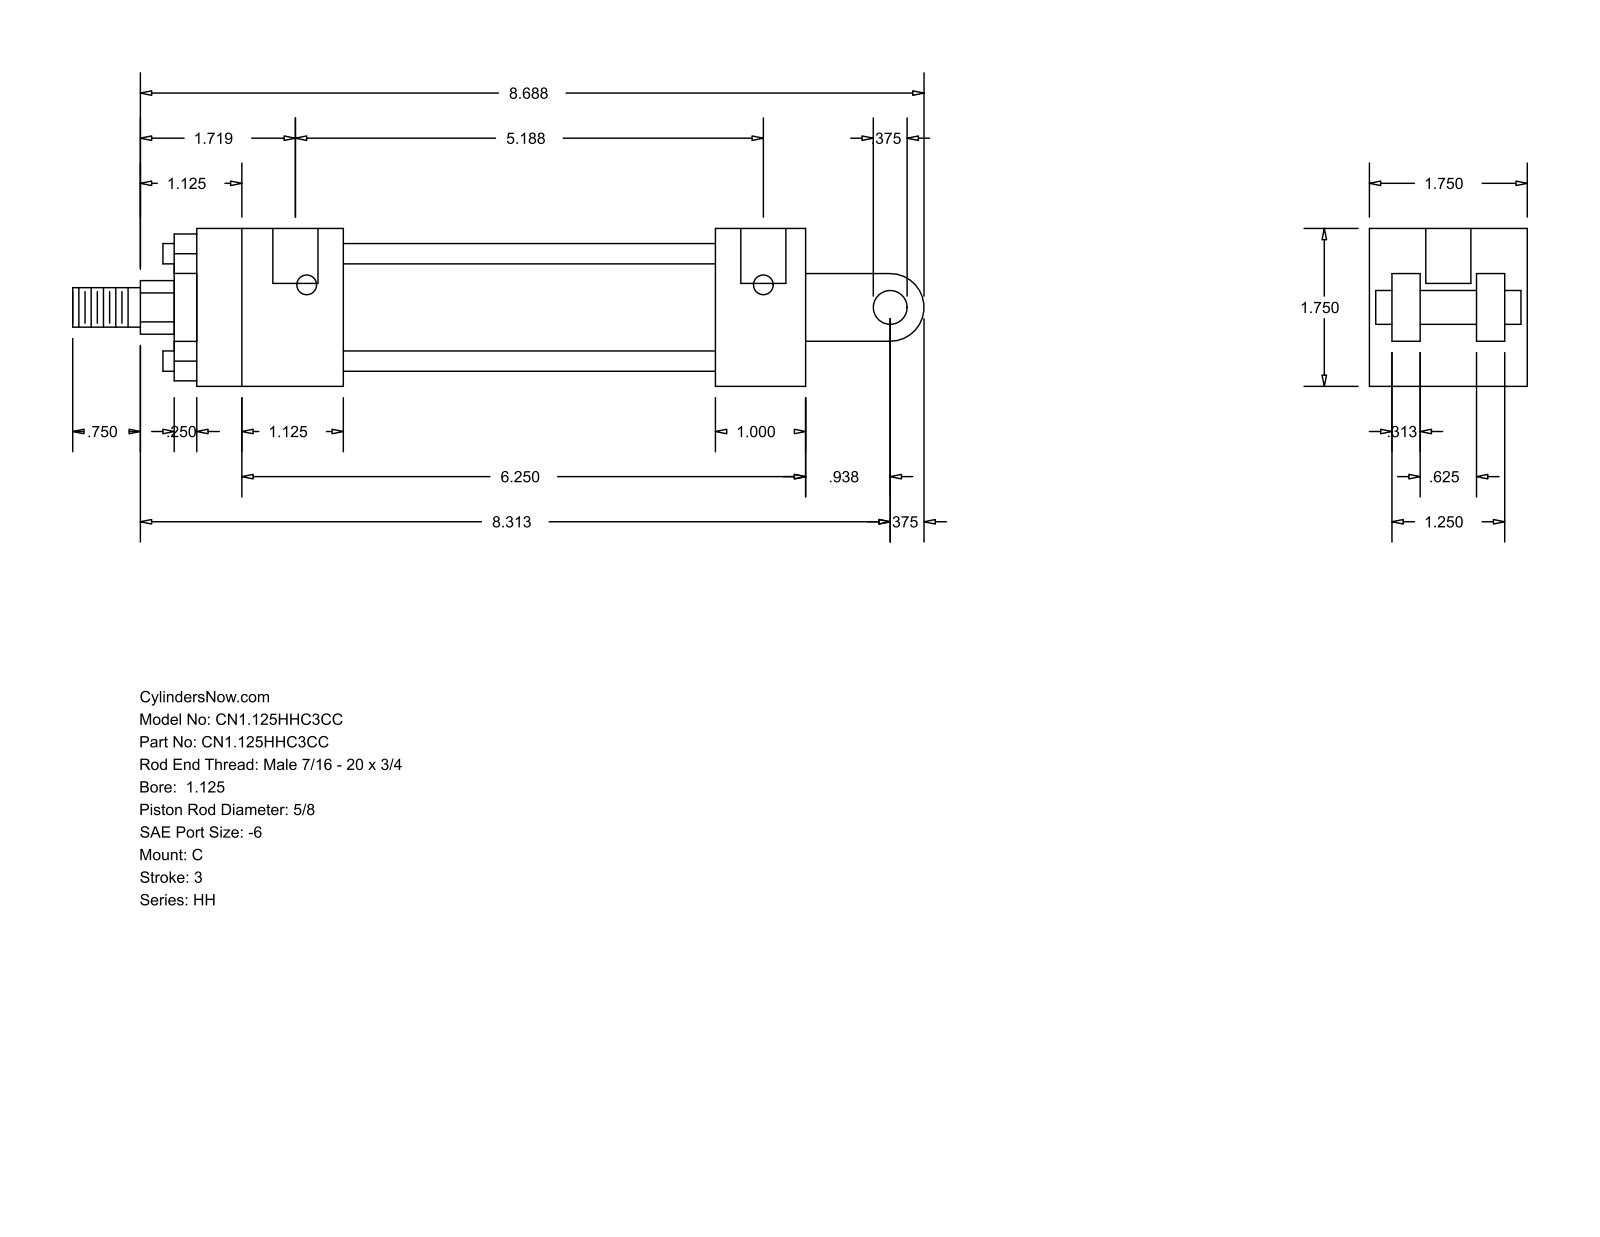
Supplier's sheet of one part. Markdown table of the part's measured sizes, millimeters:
| quantity | value |
| --- | --- |
| part name | HH_C__0112_0.625 |
| STEP written by | GSSL Pune (CONFIG_CONTROL_DESIGN) |
| units | millimeters |
| bodies | 0 solids, 99 faces (70 planar, 29 cylindrical, 0 other) |
| overall size | 239.71 × 44.45 × 44.45 |
| round holes (diameter × count) | 5.56 × 4, 12.7 × 2 |
| round bosses / shafts (diameter × count) | 5.71 × 4, 34.92 × 1, 28.57 × 1, 15.88 × 1, 11.11 × 1, 9.53 × 1 |
| partial cylindrical surfaces (radius × count) | 7.54 × 1, 9.53 × 1 |
| main face-to-face distances | 44.46, 6.35, 31.76, 14.29, 30.17, 38.11, 7.94, 23.82, 12.7, 41.27 |
| hole center spacings | 128.59, 3.17, 131.76 |
